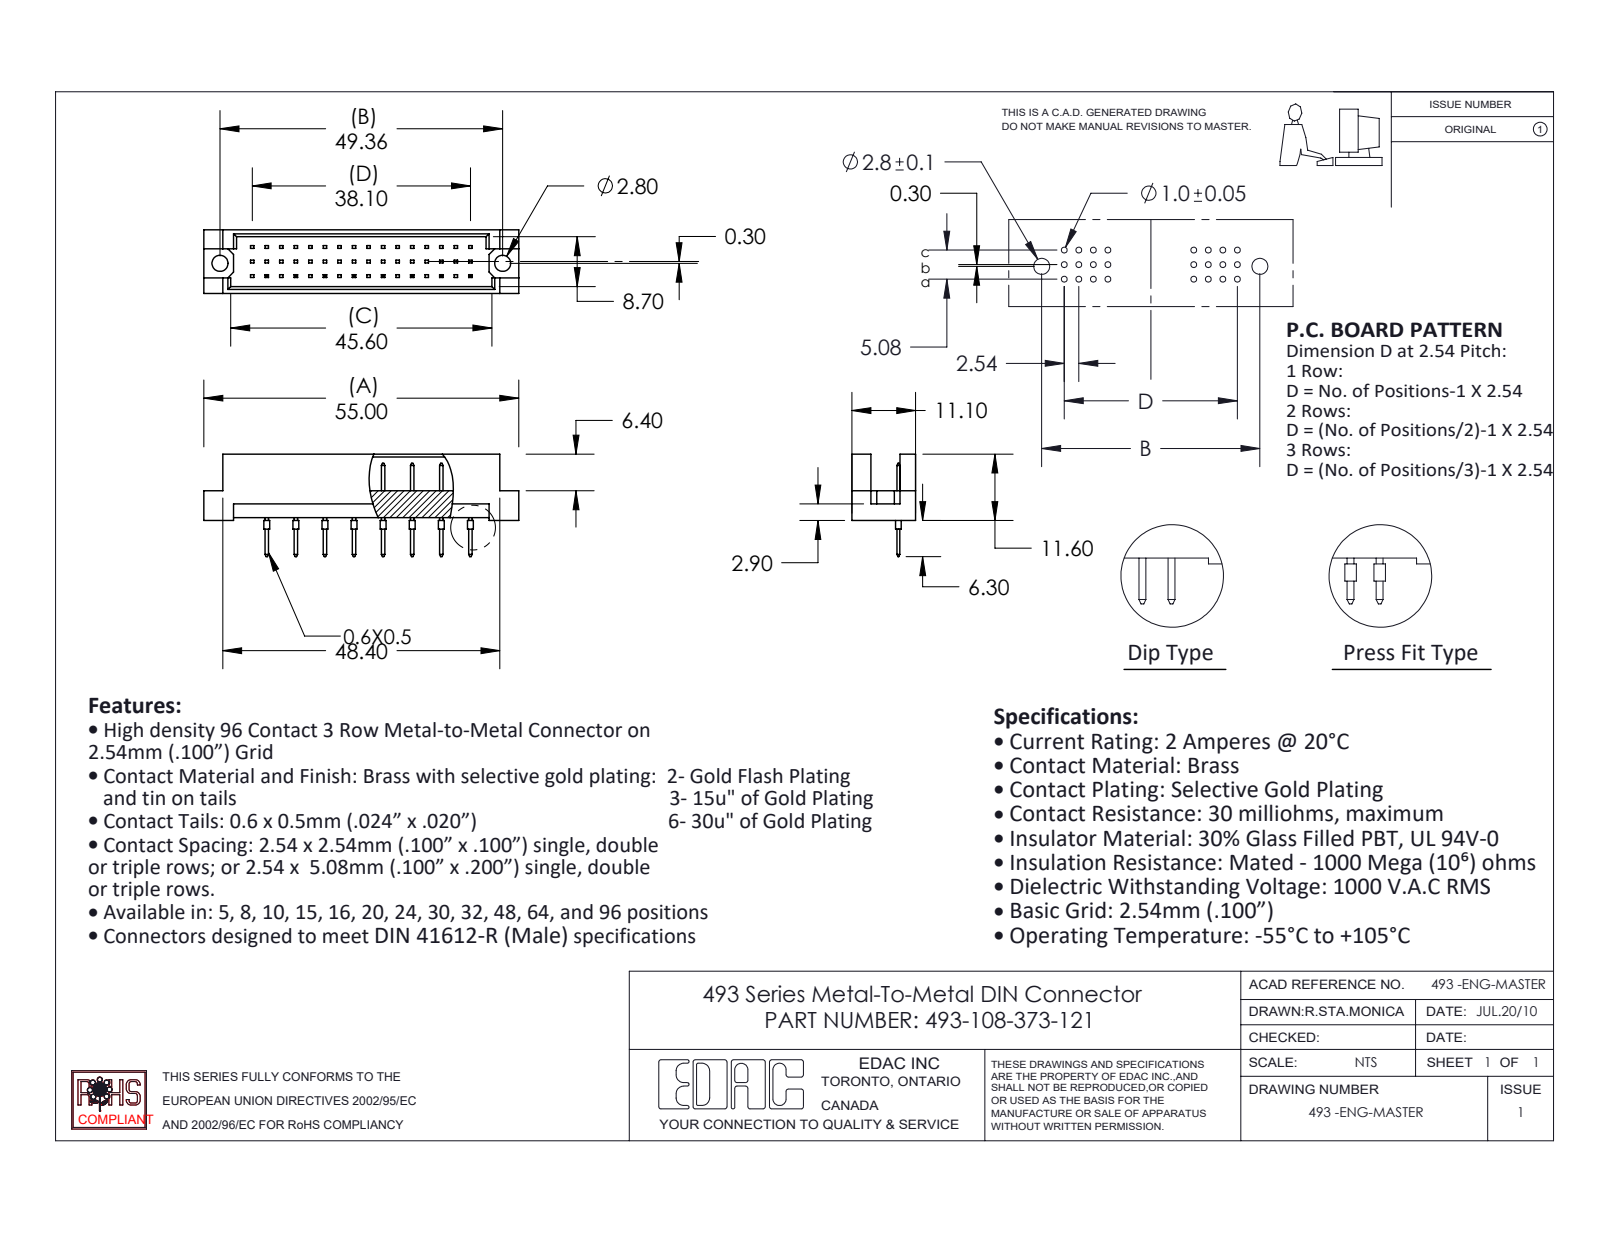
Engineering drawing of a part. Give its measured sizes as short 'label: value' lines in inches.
name: 493-108-373-121; 493-290_73; 493 Part_48
written by: SolidWorks 2020 (CONFIG_CONTROL_DESIGN)
unit: in
bodies: 9 solids, 420 faces (400 planar, 20 cylindrical, 0 other)
size: 2.165 × 0.705 × 0.437
volume: 0.202 in³; area: 6.291 in²
holes: 2× ⌀0.11
bosses: 8× ⌀0.039
face distances: 0.047, 0.39, 0.437, 0.343, 0.185, 0.02, 0.2, 0.1, 0.109, 0.328
hole spacings: 1.943
